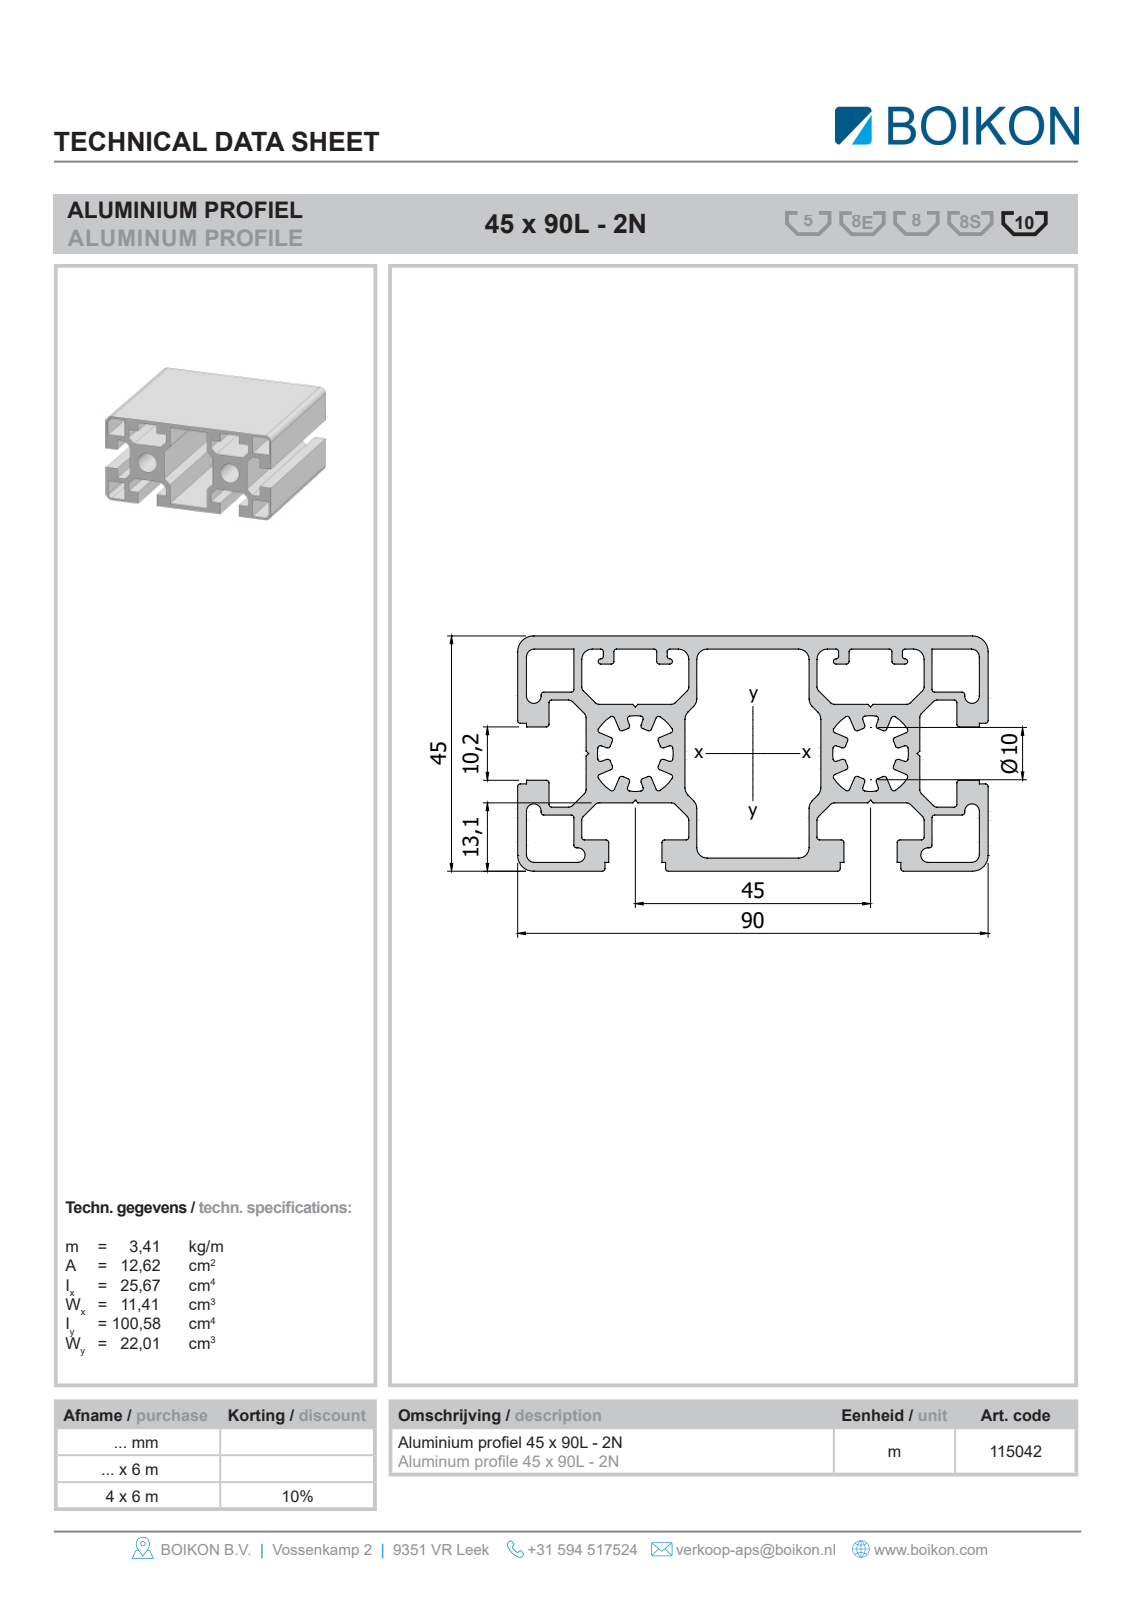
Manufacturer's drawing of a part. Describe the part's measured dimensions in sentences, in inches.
The part is named "Root; 11504245x90L-2NBOIKON0". Its 3-D file was written by "HiCAD 2013 1802.4 Build 509 (AUTOMOTIVE_DESIGN)". It is 1 solid with 104 faces: 94 planar, 10 cylindrical and 0 other. Overall it measures 39.37 by 3.543 by 1.772 inches. Its volume is 90.01 cubic inches and its surface area 1 385 square inches. Round holes: 2 of diameter 0.402. Partial cylindrical surfaces (rounded edges, fillets, slot ends): 4 of radius 0.079, 4 of radius 0.118. The main face-to-face distances are 1.772, 0.516, 1.256, 0.394, 0.169, 0.571, 0.862, 0.122, 0.236, 0.28. The hole center spacings are 1.772.
